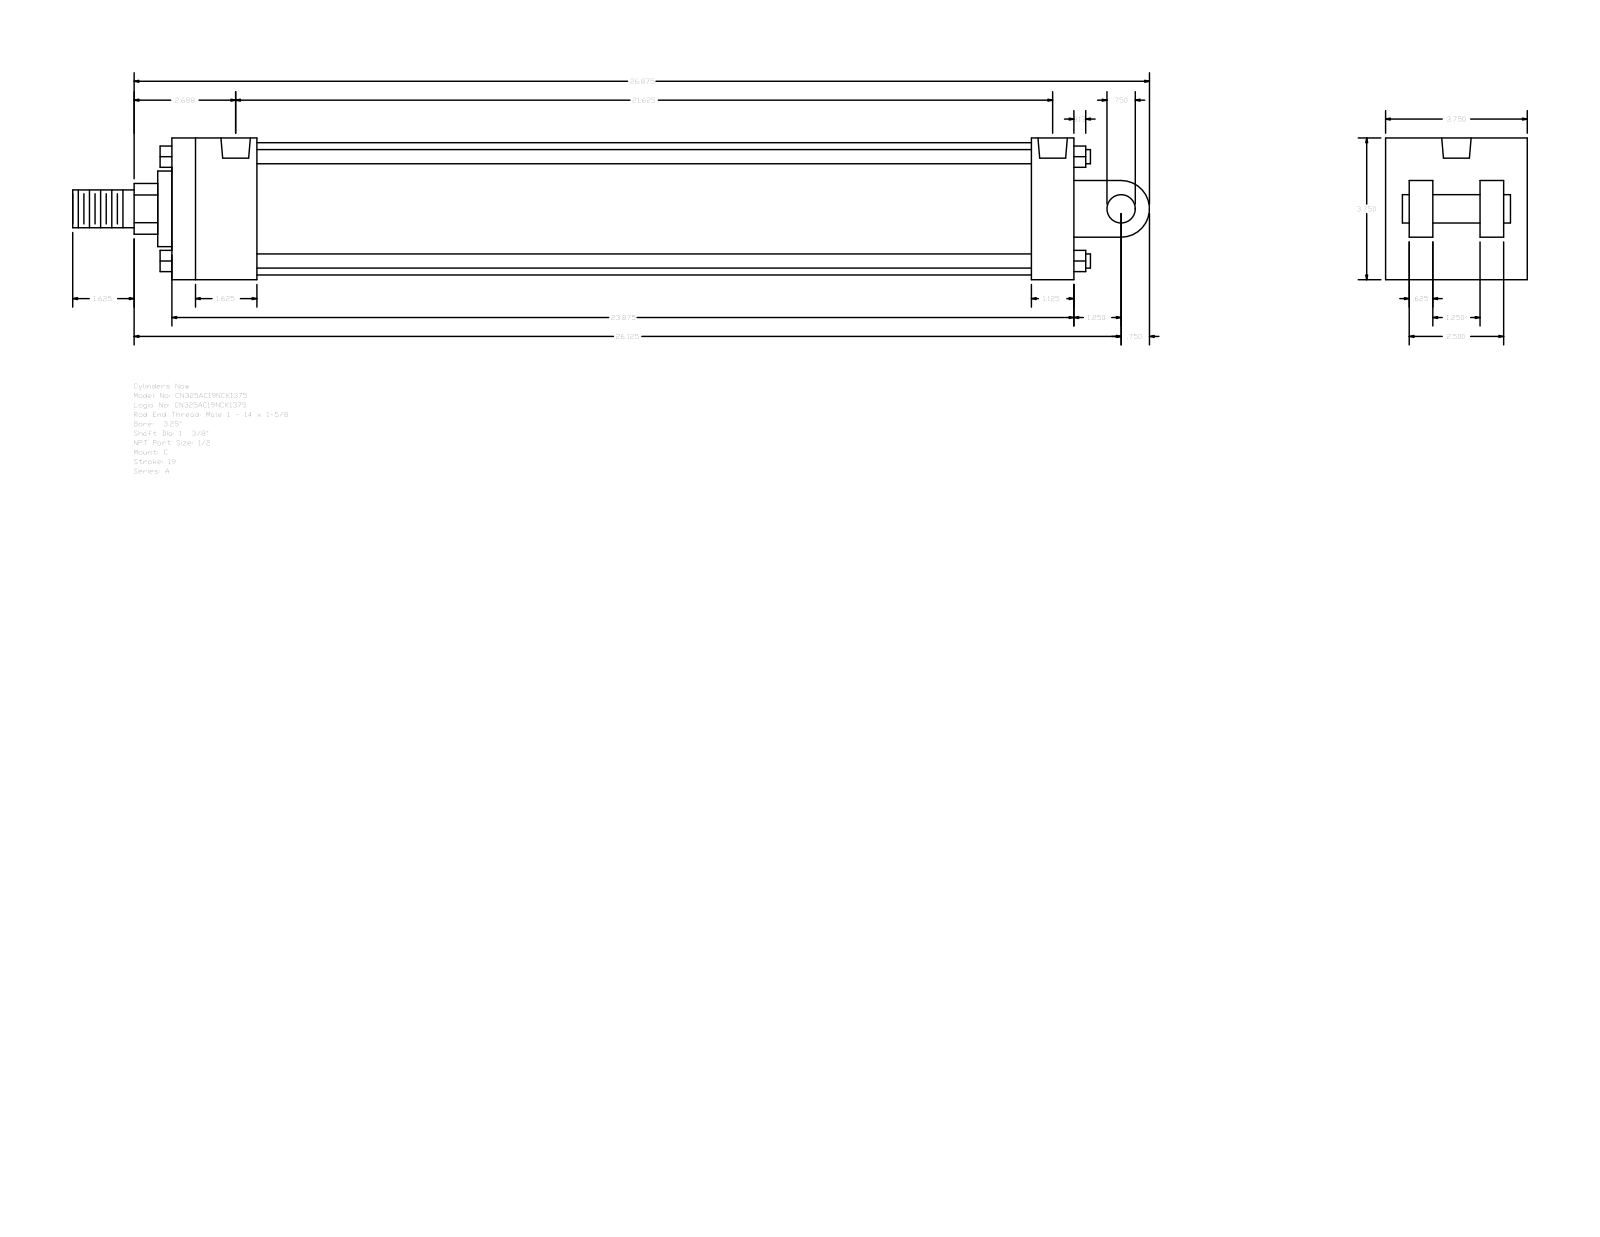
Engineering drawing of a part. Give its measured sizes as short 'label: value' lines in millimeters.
name: A_C__0325_1.375
written by: GSSL Pune (CONFIG_CONTROL_DESIGN)
unit: mm
bodies: 0 solids, 135 faces (102 planar, 33 cylindrical, 0 other)
size: 723.9 × 95.25 × 95.25
holes: 4× ⌀8.73, 2× ⌀19.77
bosses: 4× ⌀9.53, 1× ⌀88.9, 1× ⌀50.8, 1× ⌀34.92, 1× ⌀25.4, 1× ⌀19.05
rounds: 1× R17.06, 1× R19.05
face distances: 95.24, 606.43, 15.87, 63.5, 66.67, 57.15, 28.58, 31.74, 79.37, 47.63
hole spacings: 3.18, 542.92, 546.1, 549.28
